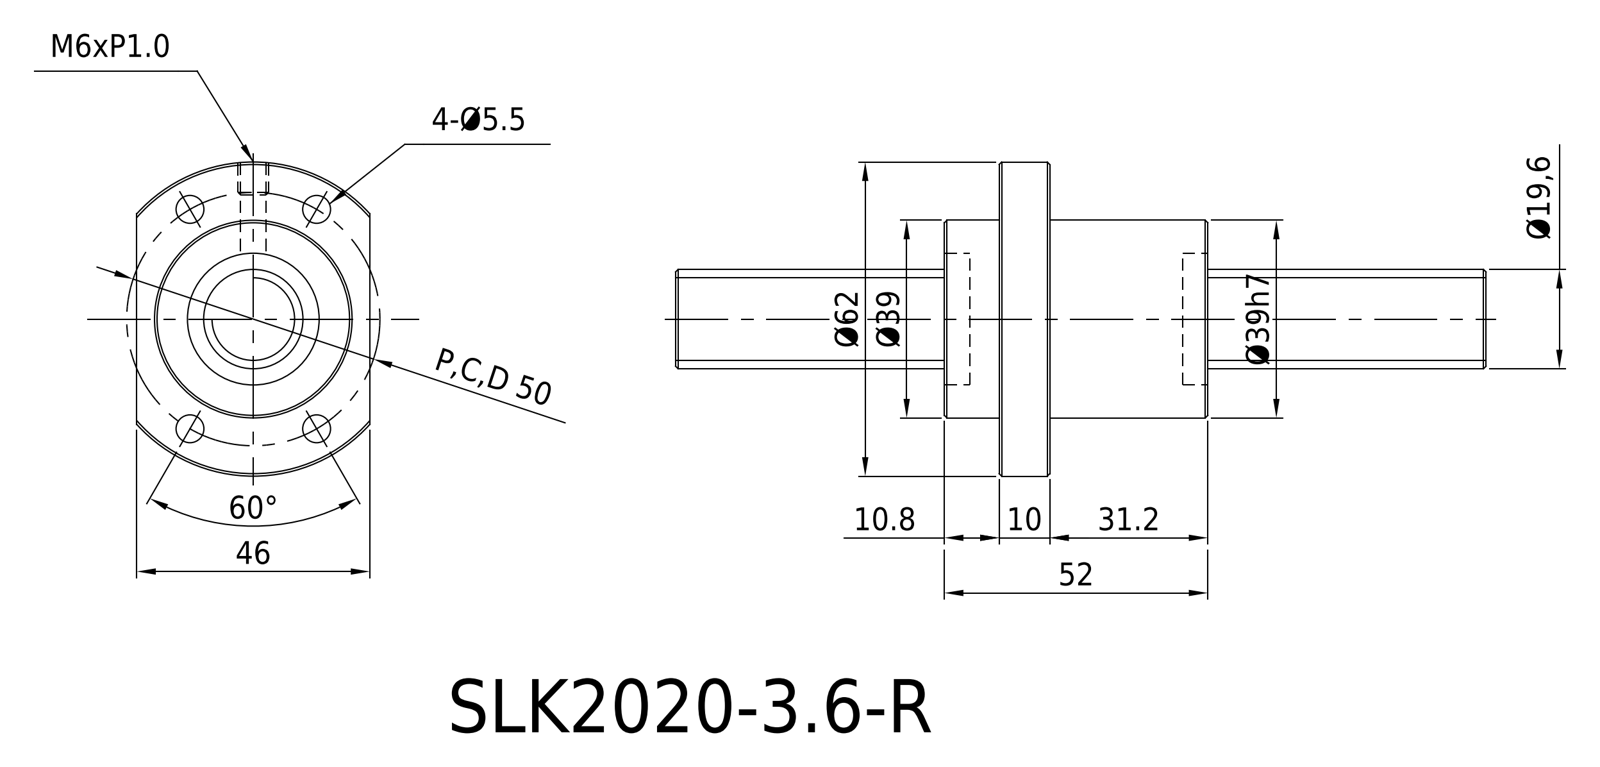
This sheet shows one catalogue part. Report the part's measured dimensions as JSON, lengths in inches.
{"part_name": "2020 STK", "step_written_by": "CATIA V5 STEP AP214 (AUTOMOTIVE_DESIGN)", "units": "inches", "bodies": {"solids": 1, "faces": 50, "planar": 6, "cylindrical": 16, "other": 28}, "overall_size": [2.441, 2.047, 1.811], "volume_in3": 3.565, "surface_area_in2": 23.36, "round_holes": [[0.217, 4], [0.787, 1]], "round_bosses_or_shafts": [[1.535, 1]], "partial_cylinders_radius": [[1.22, 1]], "face_to_face_distances": [0.394, 0.819, 0.425, 1.228, 1.622, 2.047, 1.811], "hole_center_spacings": [0.984, 1.705, 1.969]}
